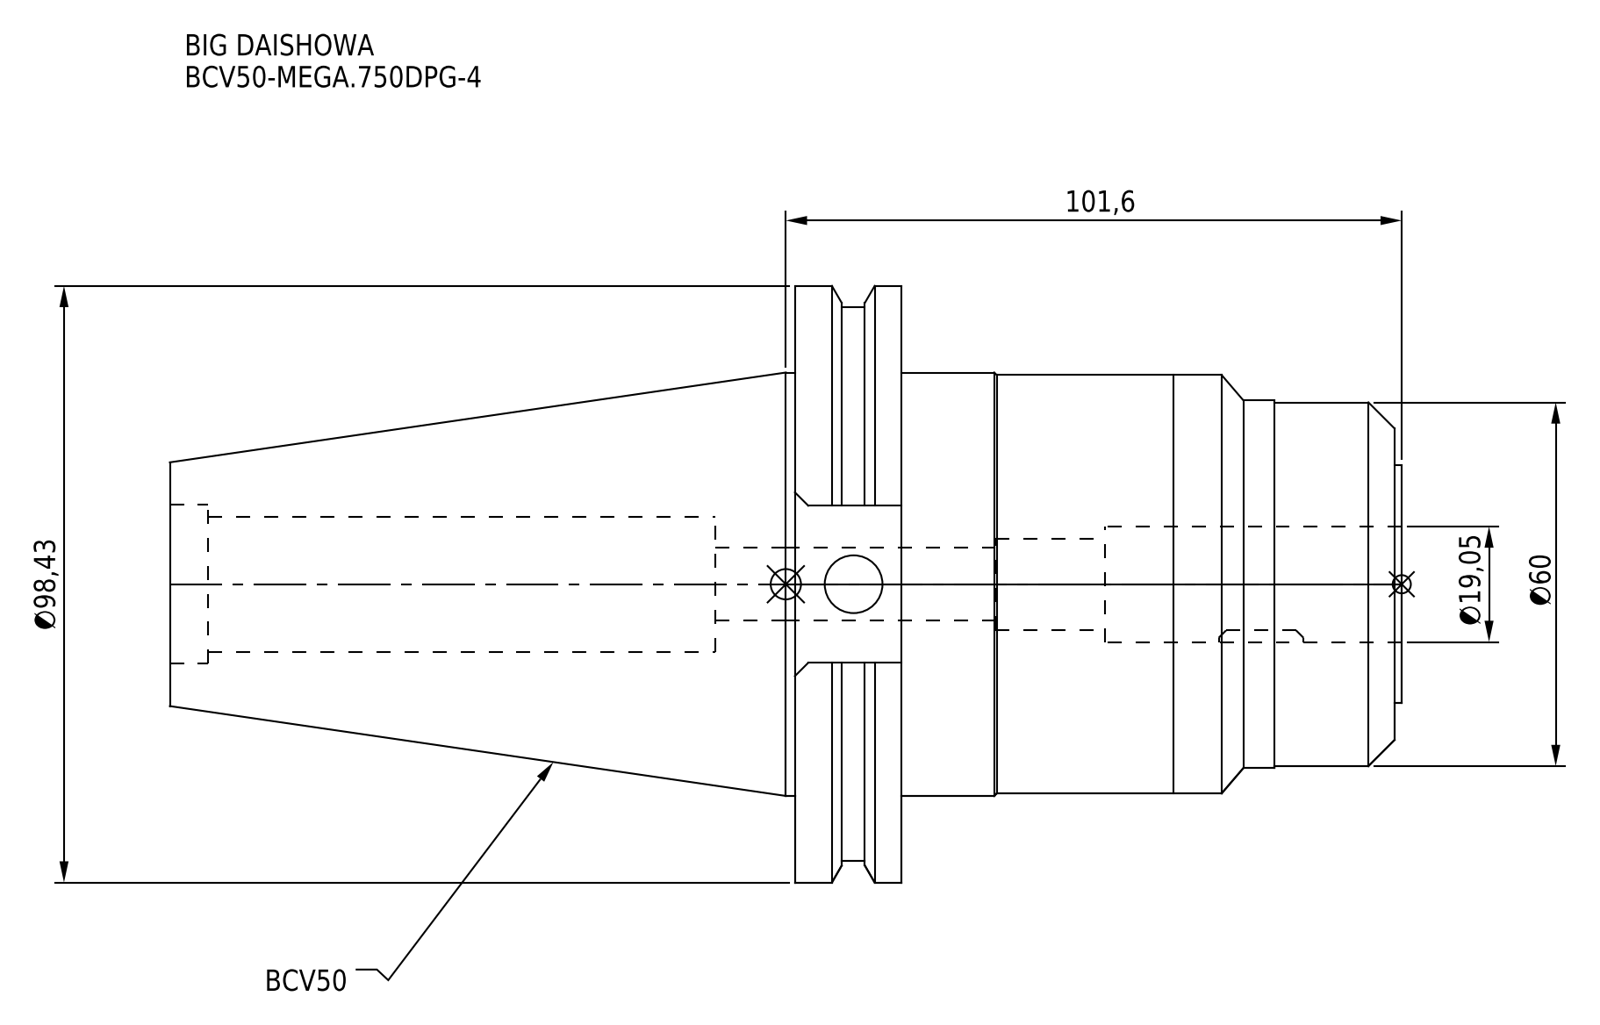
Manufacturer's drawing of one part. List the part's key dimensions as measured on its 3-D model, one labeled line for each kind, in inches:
Part name (STEP PRODUCT): BCV50-MEGA_750DPG-4
STEP written by: CREO PARAMETRIC BY PTC INC, 2016380 (AUTOMOTIVE_DESIGN)
Units: inches
Bodies: 1 solid, 69 faces (25 planar, 32 cylindrical, 12 other)
Overall size (bounding box): 8 × 3.875 × 3.738
Volume: 36.26 in³ · Surface area: 99.74 in²
Round holes (diameter × count): ⌀0.375 ×1, ⌀0.472 ×1, ⌀0.591 ×1, ⌀0.75 ×1, ⌀0.878 ×1, ⌀1.033 ×1
Round bosses / shafts (diameter × count): ⌀3.875 ×1, ⌀3.594 ×1, ⌀2.75 ×1, ⌀2.717 ×1, ⌀2.39 ×1, ⌀2.362 ×1, ⌀1.547 ×1
Main face-to-face distances: 0.691, 3.25, 3.941, 0.047, 3.203, 3.894, 8, 7.953, 4.75, 4.059
